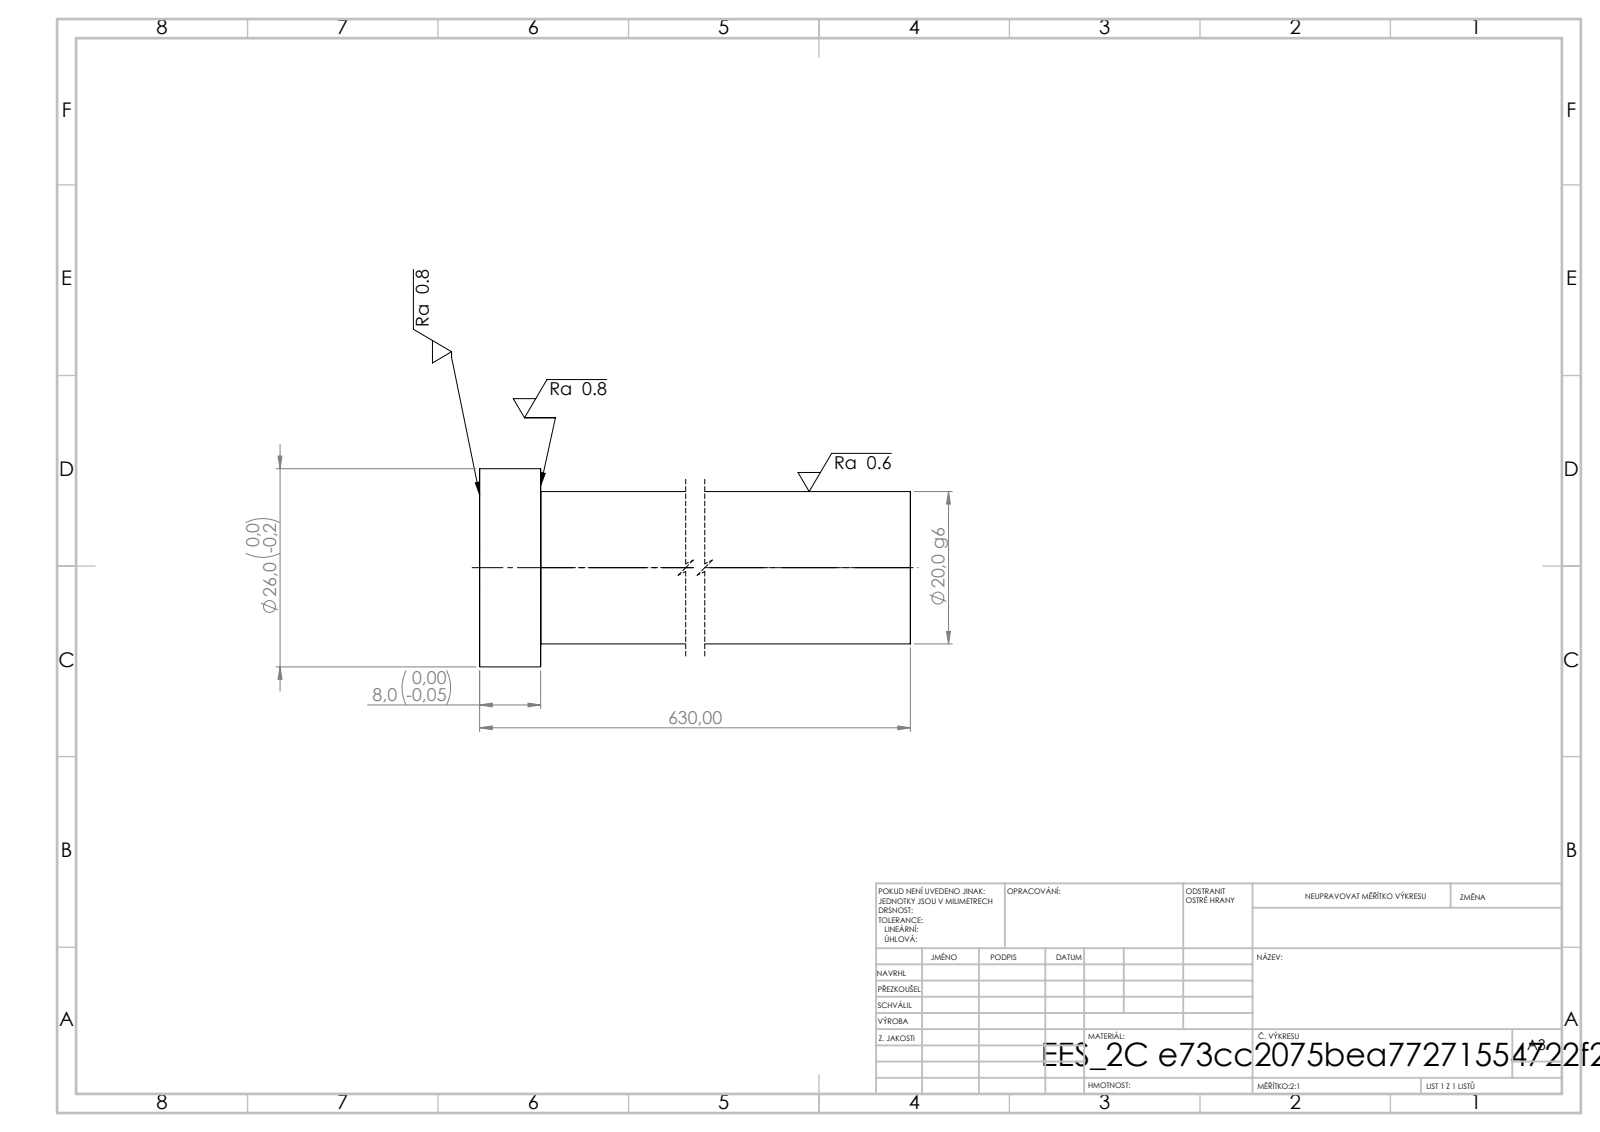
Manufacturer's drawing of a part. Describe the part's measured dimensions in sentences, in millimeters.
Its 3-D file was written by "SolidWorks 2019 (CONFIG_CONTROL_DESIGN)". It is 1 solid with 7 faces: 3 planar, 4 cylindrical and 0 other. Overall it measures 630 by 26 by 26 millimeters. Its volume is 199 654 cubic millimeters and its surface area 40 797 square millimeters. Round bosses or shafts: 1 of diameter 26, 1 of diameter 20. The main face-to-face distances are 630, 8, 622.
